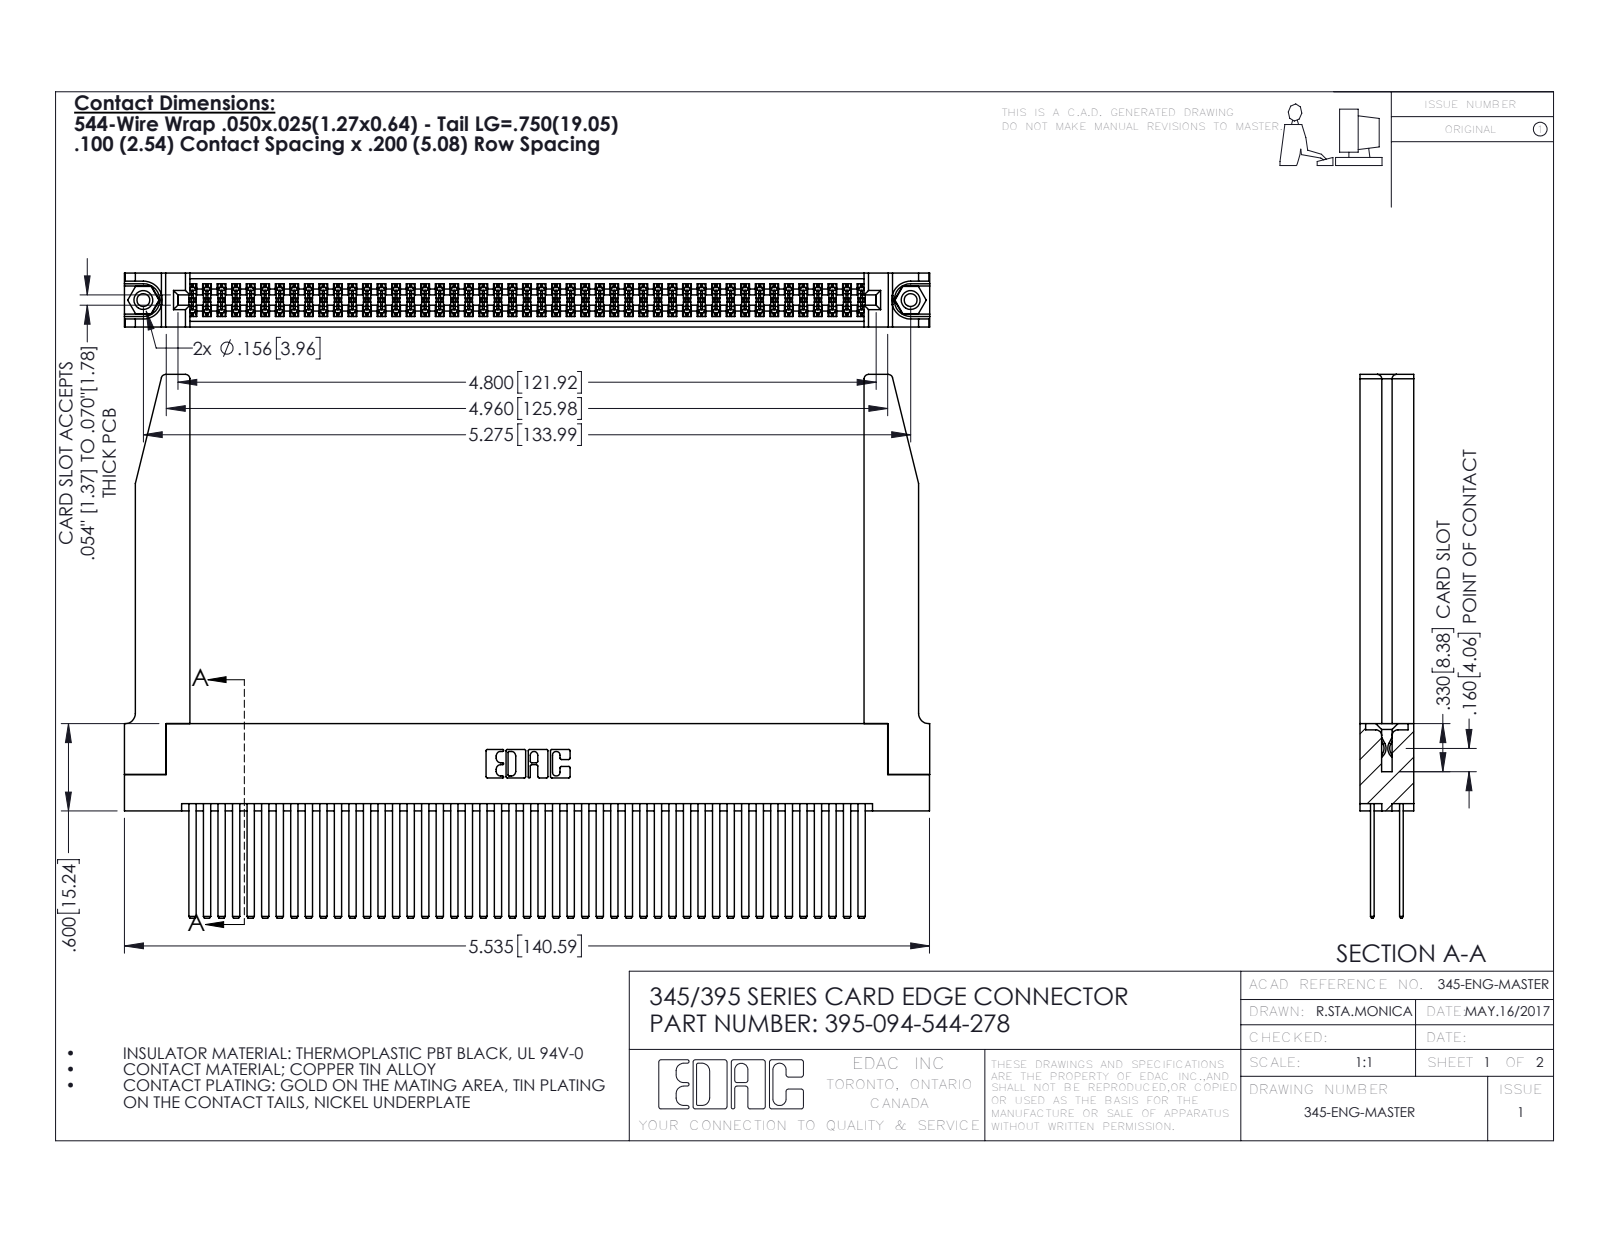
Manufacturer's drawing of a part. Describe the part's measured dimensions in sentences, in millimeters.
The part is named "345-250-001_345-250-001-102; 345 Part_Flush Mounting Lugs - 0.156 Dia-TH; 345-292-001_345-293-144; 345-220-078_345-220-078 (+1 more)". Its 3-D file was written by "SolidWorks 2016 (CONFIG_CONTROL_DESIGN)". It is 99 solids with 4496 faces: 2948 planar, 1496 cylindrical and 52 other. Overall it measures 140.6 by 94.9 by 9.4 millimeters. Its volume is 22 790 cubic millimeters and its surface area 33 010 square millimeters. Round holes: 2 of diameter 2.3, 2 of diameter 3.2, 2 of diameter 4, 1 of diameter 1.6. Round bosses or shafts: 2 of diameter 3.9. Partial cylindrical surfaces (rounded edges, fillets, slot ends): 141 of radius 0.2, 22 of radius 0.3, 8 of radius 0.8, 6 of radius 0.2, 6 of radius 0.8, 3 of radius 0.7, 2 of radius 0.4, 2 of radius 0.5. The main face-to-face distances are 1.8, 7.6, 5.1, 2.5, 6.9, 0.6, 9.4, 5.7, 4.4, 3.8. The hole center spacings are 6.9, 128, 134.
